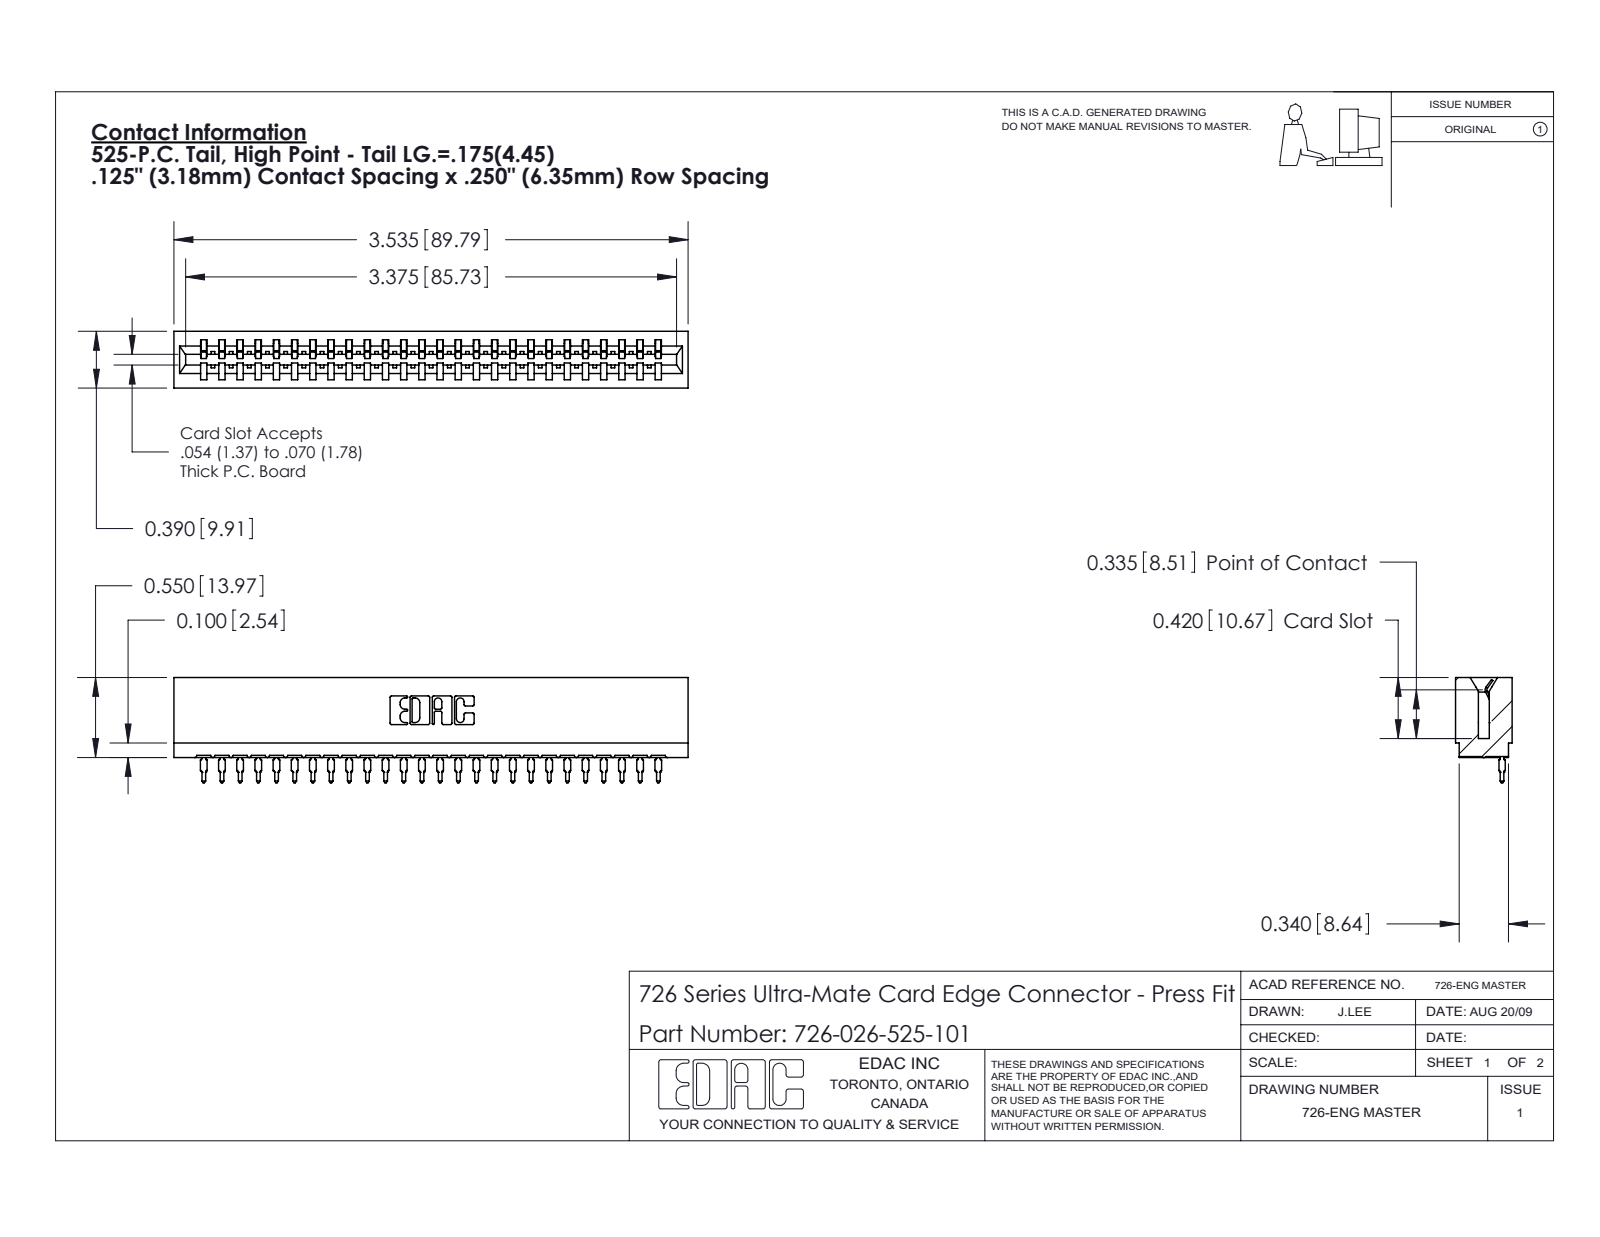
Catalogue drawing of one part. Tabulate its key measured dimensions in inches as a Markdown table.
| quantity | value |
| --- | --- |
| part name | 726-026-525-101; 746-292-001_525; 726 Part_.515 Slot Depth - 01 |
| STEP written by | SolidWorks 2020 (CONFIG_CONTROL_DESIGN) |
| units | inches |
| bodies | 27 solids, 2905 faces (1693 planar, 536 cylindrical, 676 other) |
| overall size | 3.535 × 0.724 × 0.39 |
| volume | 0.493 in³ |
| surface area | 18.55 in² |
| partial cylindrical surfaces (radius × count) | 0.021 × 52, 0.015 × 27, 0.01 × 22, 0.007 × 6, 0.031 × 6, 0.005 × 4, 0.011 × 4, 0.026 × 3 |
| main face-to-face distances | 0.057, 0.333, 0.39, 0.25, 0.025, 0.307, 0.5, 0.125, 0.75, 0.275 |
